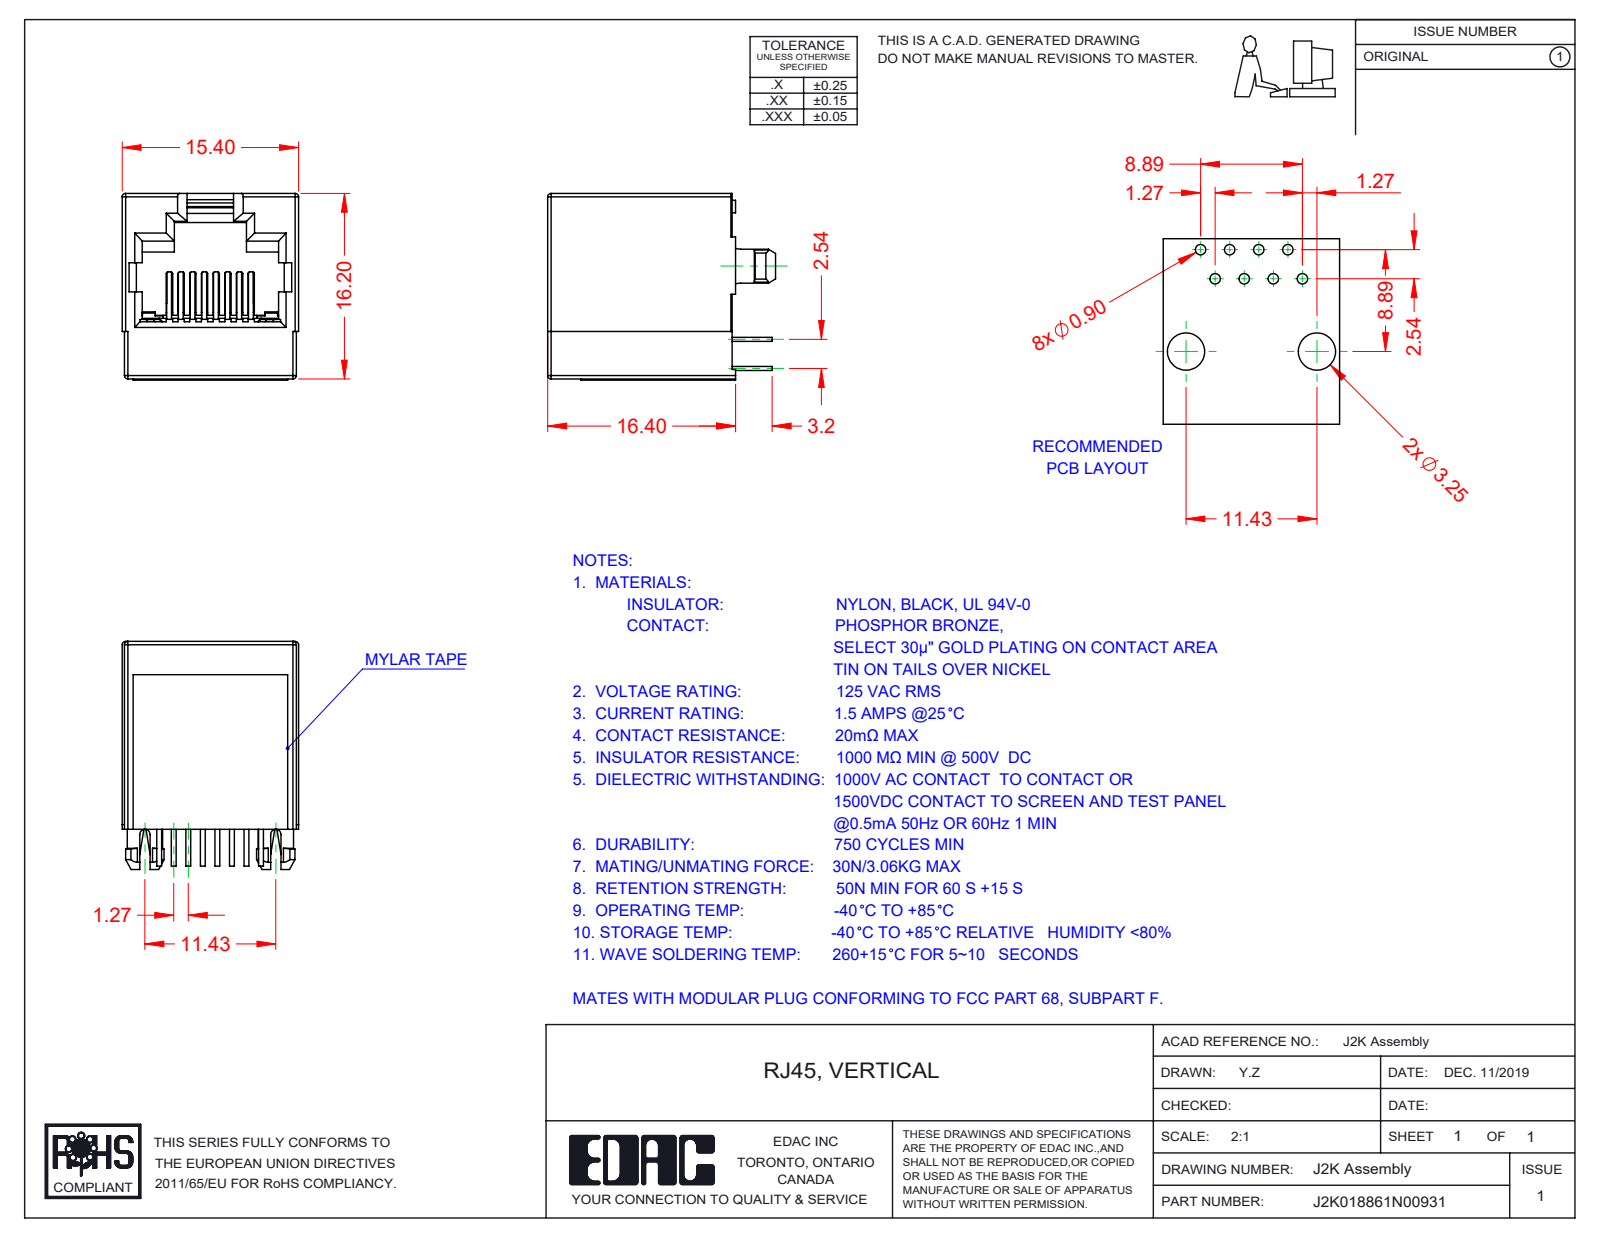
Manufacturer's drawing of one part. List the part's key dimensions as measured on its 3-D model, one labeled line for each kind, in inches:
Part name (STEP PRODUCT): RJ2K018861N00931; 2K Insulator; 2K Contacts; 2K Mylar Tape (+1 more)
STEP written by: SolidWorks 2016 (CONFIG_CONTROL_DESIGN)
Units: inches
Bodies: 11 solids, 729 faces (592 planar, 113 cylindrical, 24 other)
Overall size (bounding box): 0.783 × 0.642 × 0.606
Volume: 0.152 in³ · Surface area: 6.715 in²
Round bosses / shafts (diameter × count): ⌀0.122 ×2, ⌀0.043 ×2
Partial cylindrical surfaces — rounded edges, fillets, slot ends (radius × count): R0.006 ×16, R0.012 ×10, R0.02 ×3, R0.004 ×2, R0.008 ×2, R0.018 ×2, R0.024 ×2, R0.037 ×2
Main face-to-face distances: 0.638, 0.606, 0.642, 0.551, 0.055, 0.047, 0.543, 0.598, 0.02, 0.051
